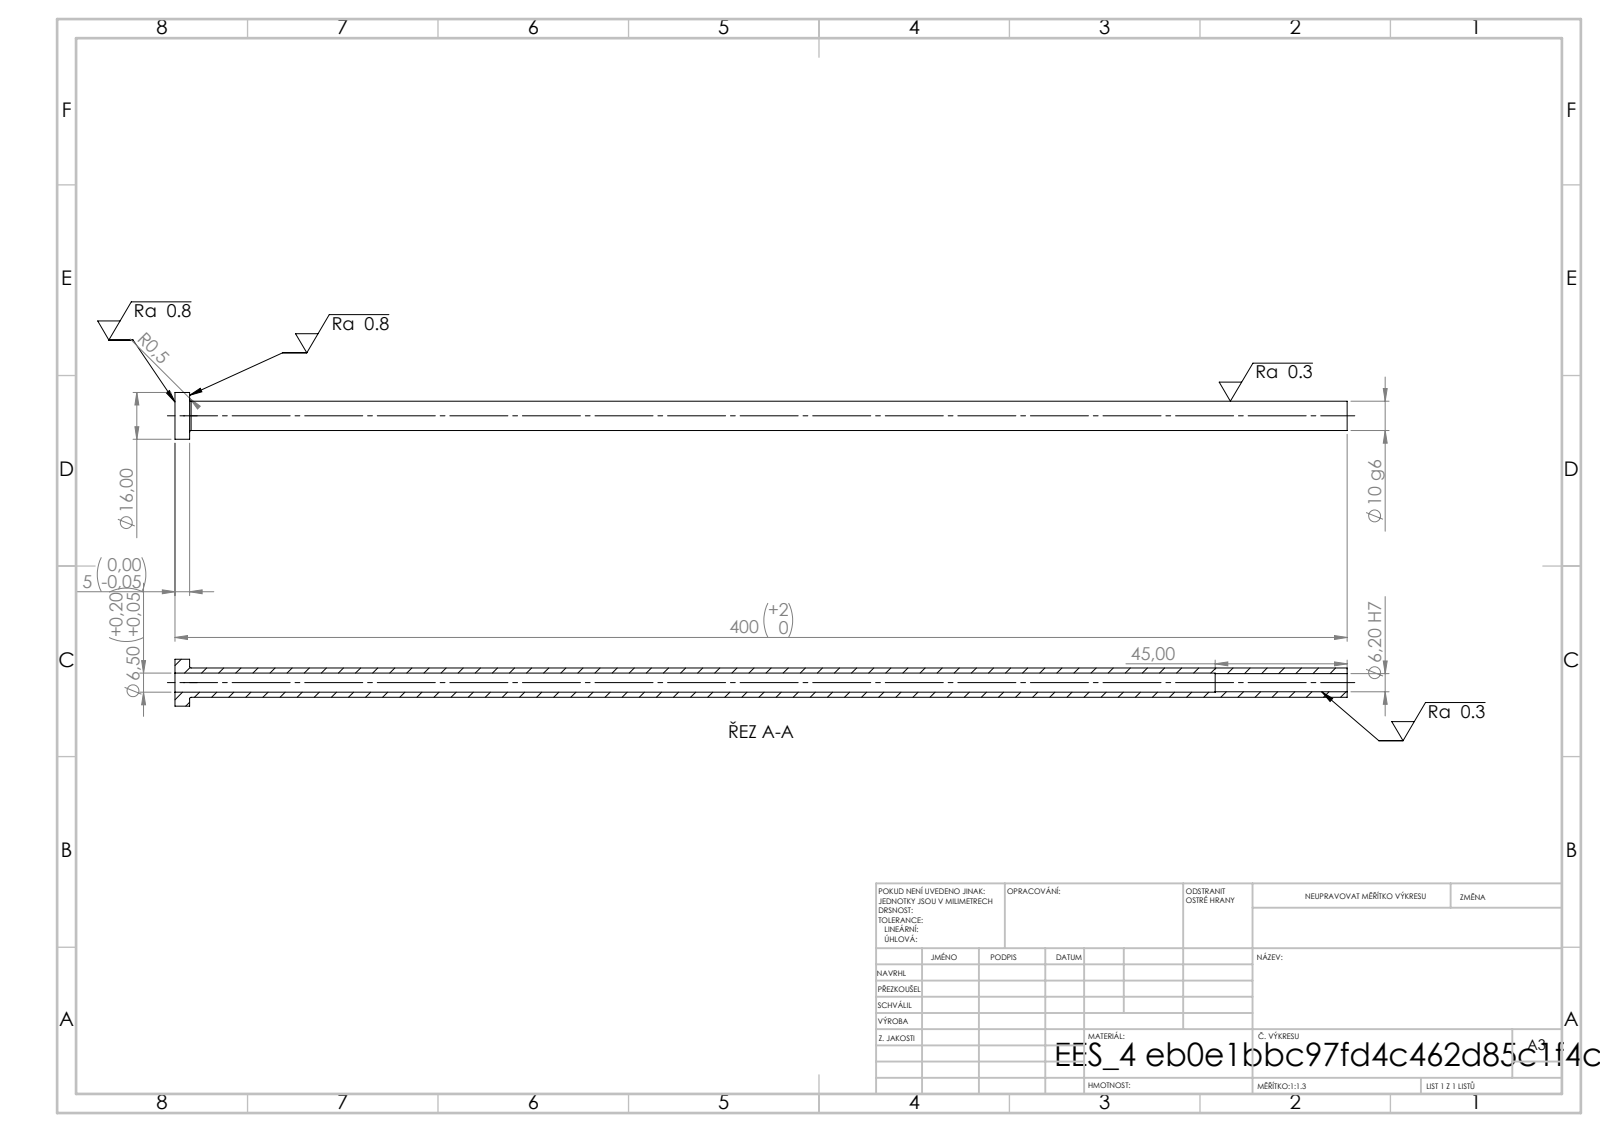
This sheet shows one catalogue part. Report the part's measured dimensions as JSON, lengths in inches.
{"step_written_by": "SolidWorks 2019 (CONFIG_CONTROL_DESIGN)", "units": "inches", "bodies": {"solids": 1, "faces": 14, "planar": 4, "cylindrical": 8, "other": 2}, "overall_size": [15.748, 0.63, 0.63], "volume_in3": 1.153, "surface_area_in2": 32.74, "round_holes": [[0.244, 1], [0.256, 1]], "round_bosses_or_shafts": [[0.63, 1], [0.394, 1]], "face_to_face_distances": [0.197, 15.748, 15.551, 13.976, 13.78, 1.772]}
